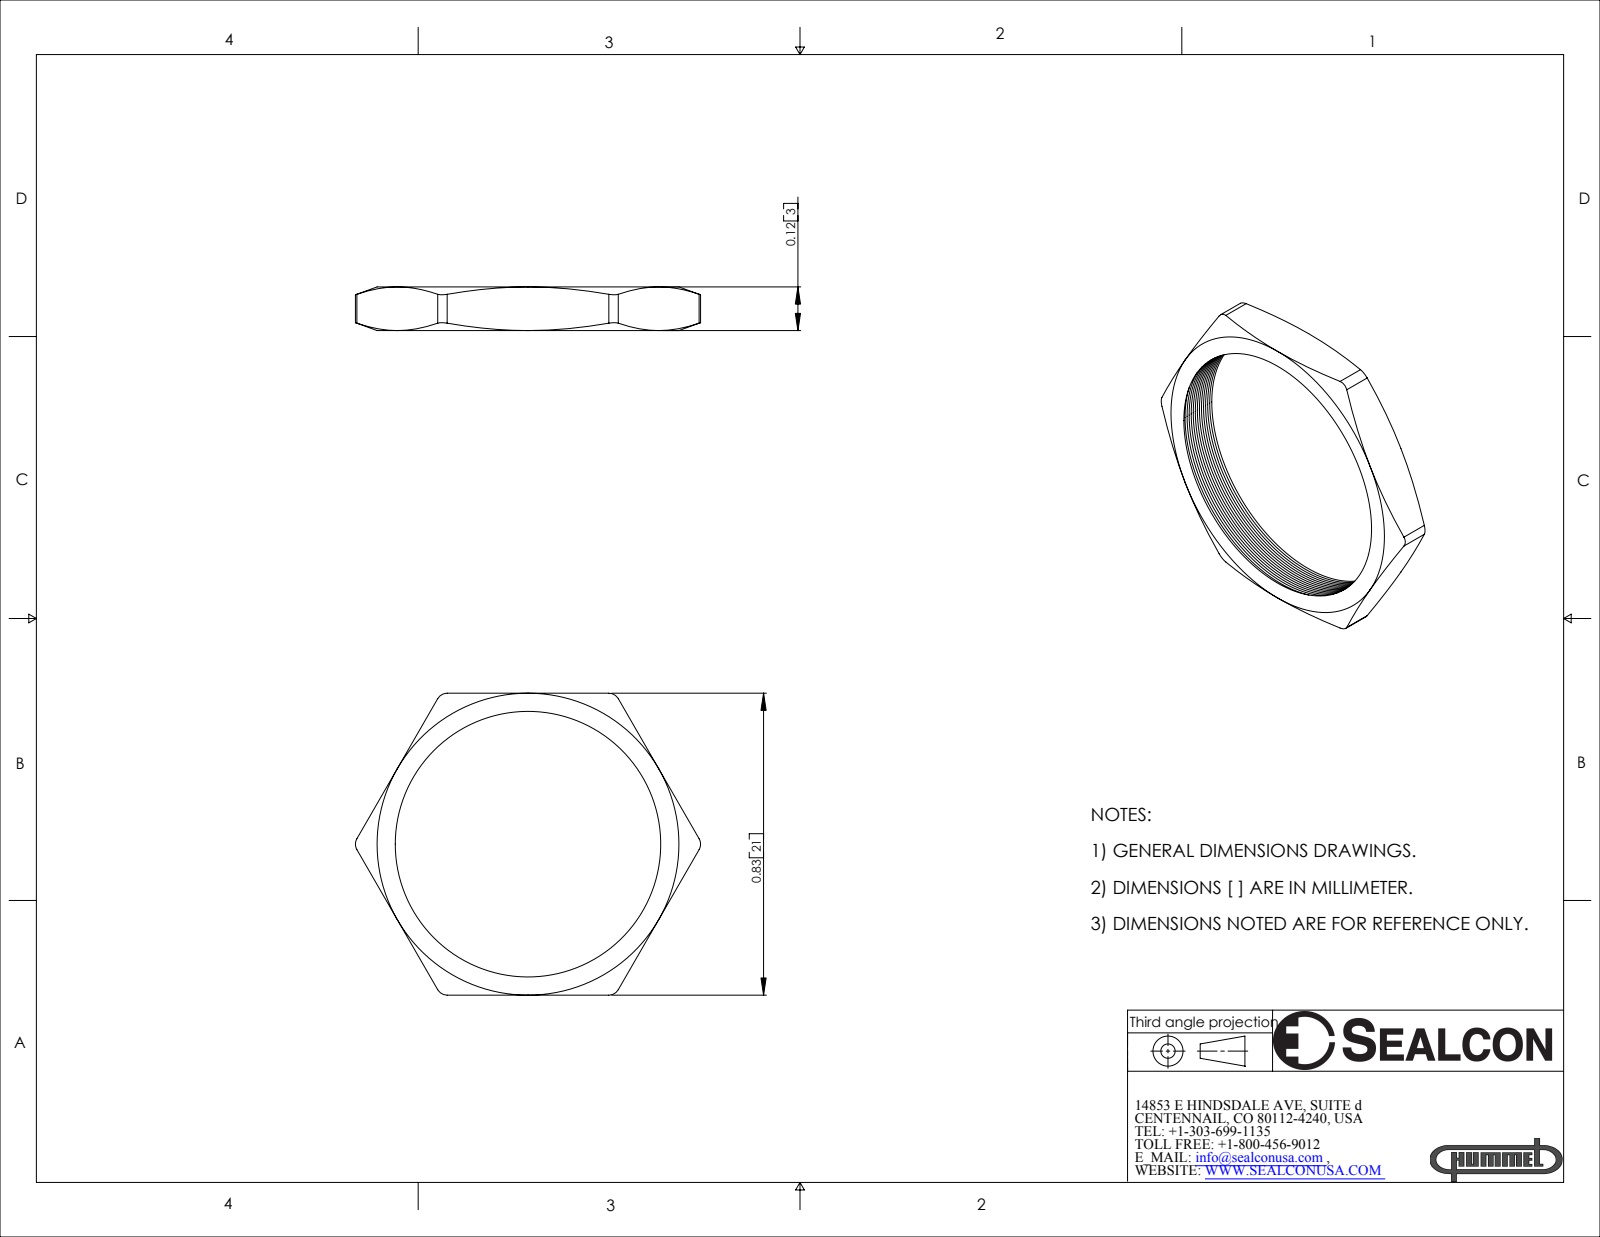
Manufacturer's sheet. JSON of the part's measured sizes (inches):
{"part_name": "NP-11-BR", "step_written_by": "SolidWorks 2007 (CONFIG_CONTROL_DESIGN)", "units": "inches", "bodies": {"solids": 1, "faces": 87, "planar": 8, "cylindrical": 7, "other": 72}, "overall_size": [0.949, 0.83, 0.12], "volume_in3": 0.017, "surface_area_in2": 1.195, "partial_cylinders_radius": [[0.03, 6]], "face_to_face_distances": [0.83, 0.12]}
